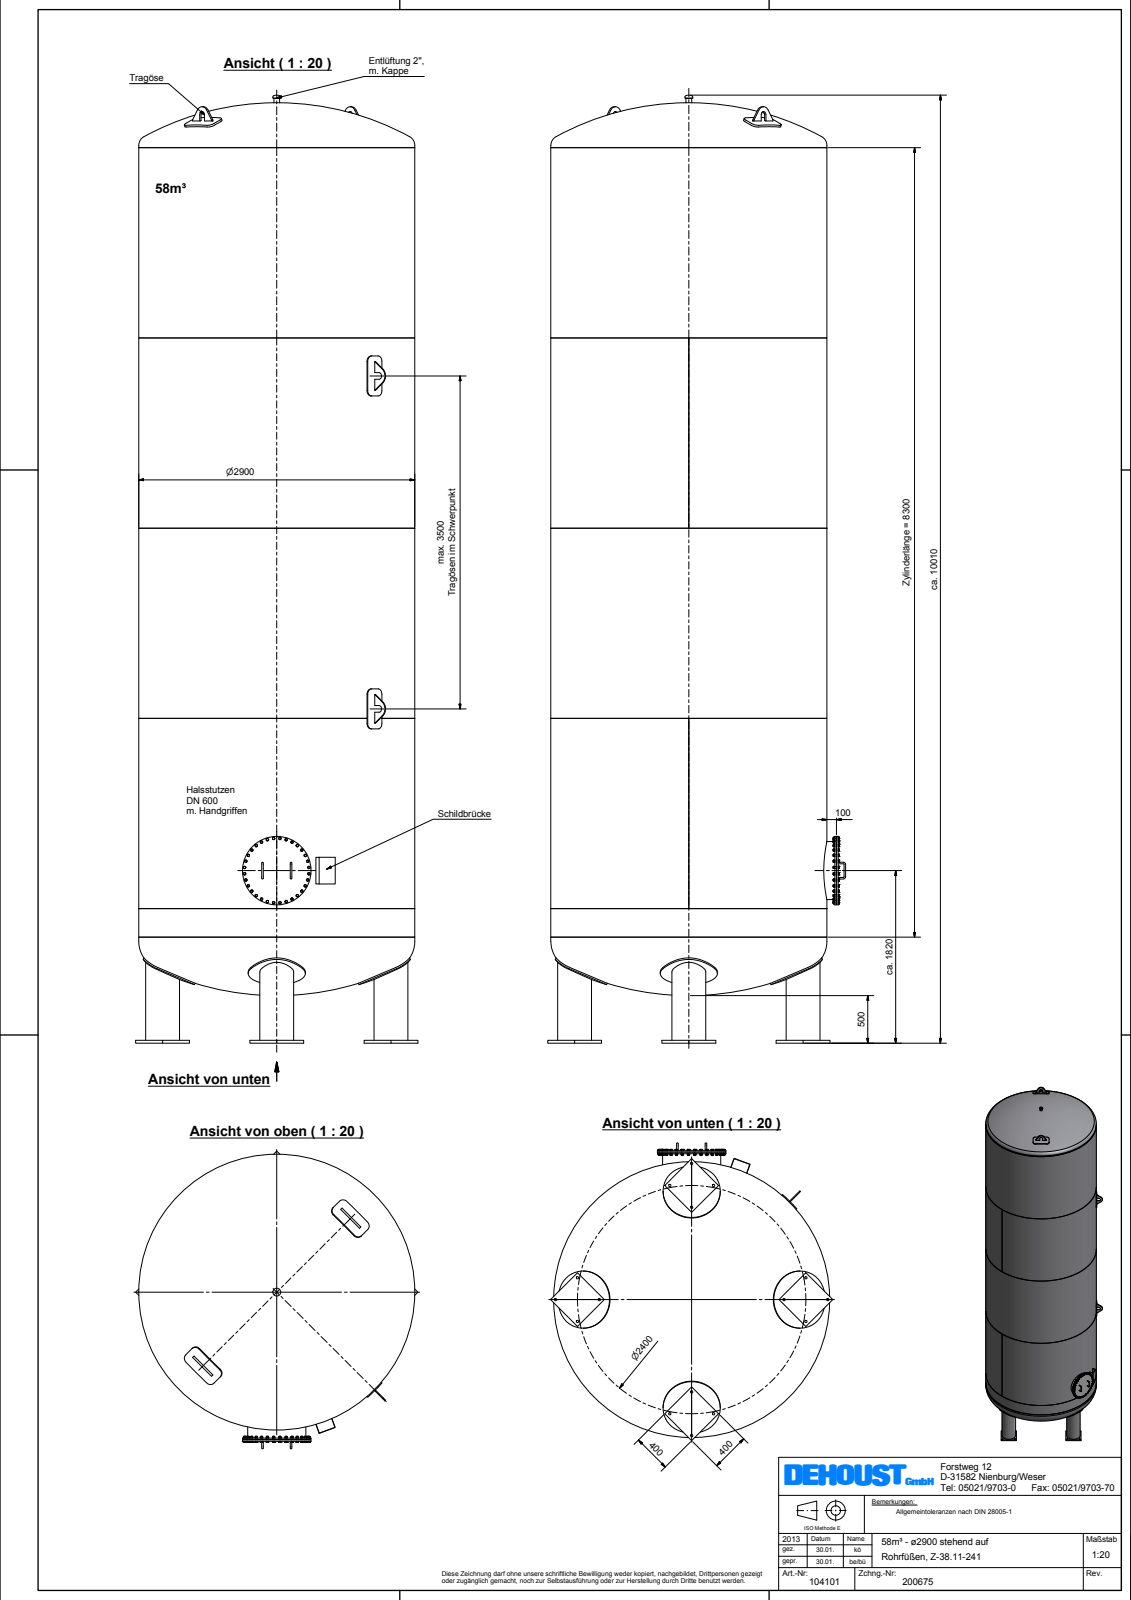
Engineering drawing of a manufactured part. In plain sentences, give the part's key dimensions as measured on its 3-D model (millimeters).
The part is named "Beh\\S\\dlter_Z-38_11-241_2900_058_KV". Its 3-D file was written by "Autodesk Inventor 2012 (AUTOMOTIVE_DESIGN)". It is 5 solids with 1136 faces: 640 planar, 168 cylindrical and 328 other. Overall it measures 9967 by 3129.84 by 2965.68 millimeters. Its volume is 3 364 000 000 cubic millimeters and its surface area 192 100 000 square millimeters. Round holes: 4 of diameter 230, 4 of diameter 336.6, 1 of diameter 598, 1 of diameter 2880, 1 of diameter 2886, 1 of diameter 2888. Round bosses or shafts: 38 of diameter 16, 32 of diameter 22.5, 4 of diameter 600, 4 of diameter 355.6, 1 of diameter 2900, 1 of diameter 720, 1 of diameter 660, 1 of diameter 610. Partial cylindrical surfaces (rounded edges, fillets, slot ends): 16 of radius 56, 4 of radius 35, 4 of radius 85, 1 of radius 1460. The main face-to-face distances are 1114.04, 30, 1084.04, 35, 16, 19, 3.02, 399.94, 1696.8, 10. The hole center spacings are 1200, 1697.06, 2400.
